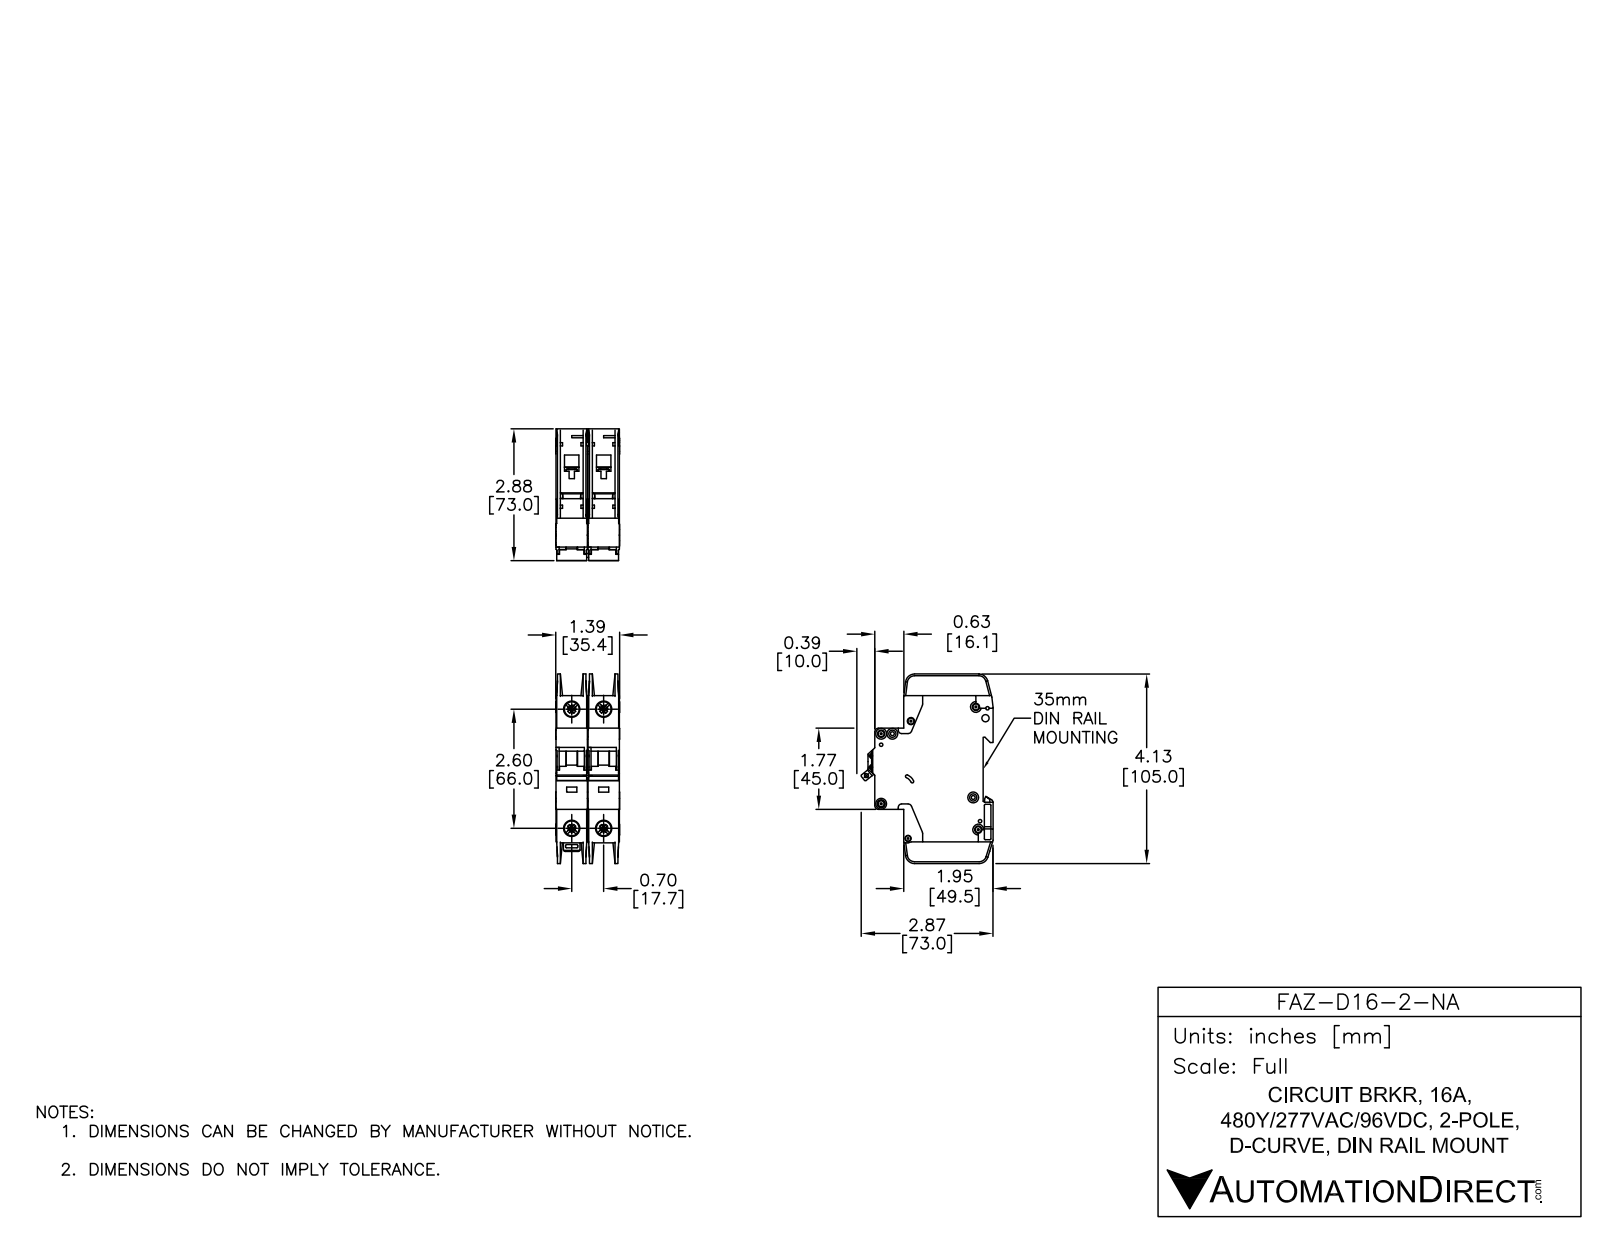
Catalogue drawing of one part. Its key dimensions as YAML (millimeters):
part_name: "FAZ-D16-2-NA"
step_written_by: "SolidWorks 2014 (AUTOMOTIVE_DESIGN)"
units: millimeters
bodies: {solids: 6, faces: 1568, planar: 818, cylindrical: 526, other: 224}
overall_size: [105, 73.04, 35.4]
volume: 155390
surface_area: 49479
round_holes:
  - {diameter: 3.6, count: 7}
  - {diameter: 7.15, count: 4}
  - {diameter: 8.2, count: 4}
  - {diameter: 1.09, count: 2}
  - {diameter: 1.5, count: 2}
  - {diameter: 4, count: 2}
  - {diameter: 1.9, count: 1}
  - {diameter: 2.15, count: 1}
  - {diameter: 2.2, count: 1}
  - {diameter: 2.55, count: 1}
  - {diameter: 3.3, count: 1}
  - {diameter: 3.4, count: 1}
round_bosses_or_shafts:
  - {diameter: 6, count: 7}
  - {diameter: 2.5, count: 2}
partial_cylinders:
  - {radius: 0.25, count: 47}
  - {radius: 0.5, count: 24}
  - {radius: 1, count: 18}
  - {radius: 2, count: 12}
  - {radius: 5, count: 5}
  - {radius: 1.8, count: 4}
  - {radius: 4, count: 4}
  - {radius: 0.2, count: 2}
face_to_face_distances: [17.7, 17.5, 0.7, 15.05, 2.45, 1.75, 15.75, 13.3, 35.2, 17]
hole_center_spacings: [6.2, 17.7, 66, 68.33, 5.19, 6.1, 8.19, 8.56]
